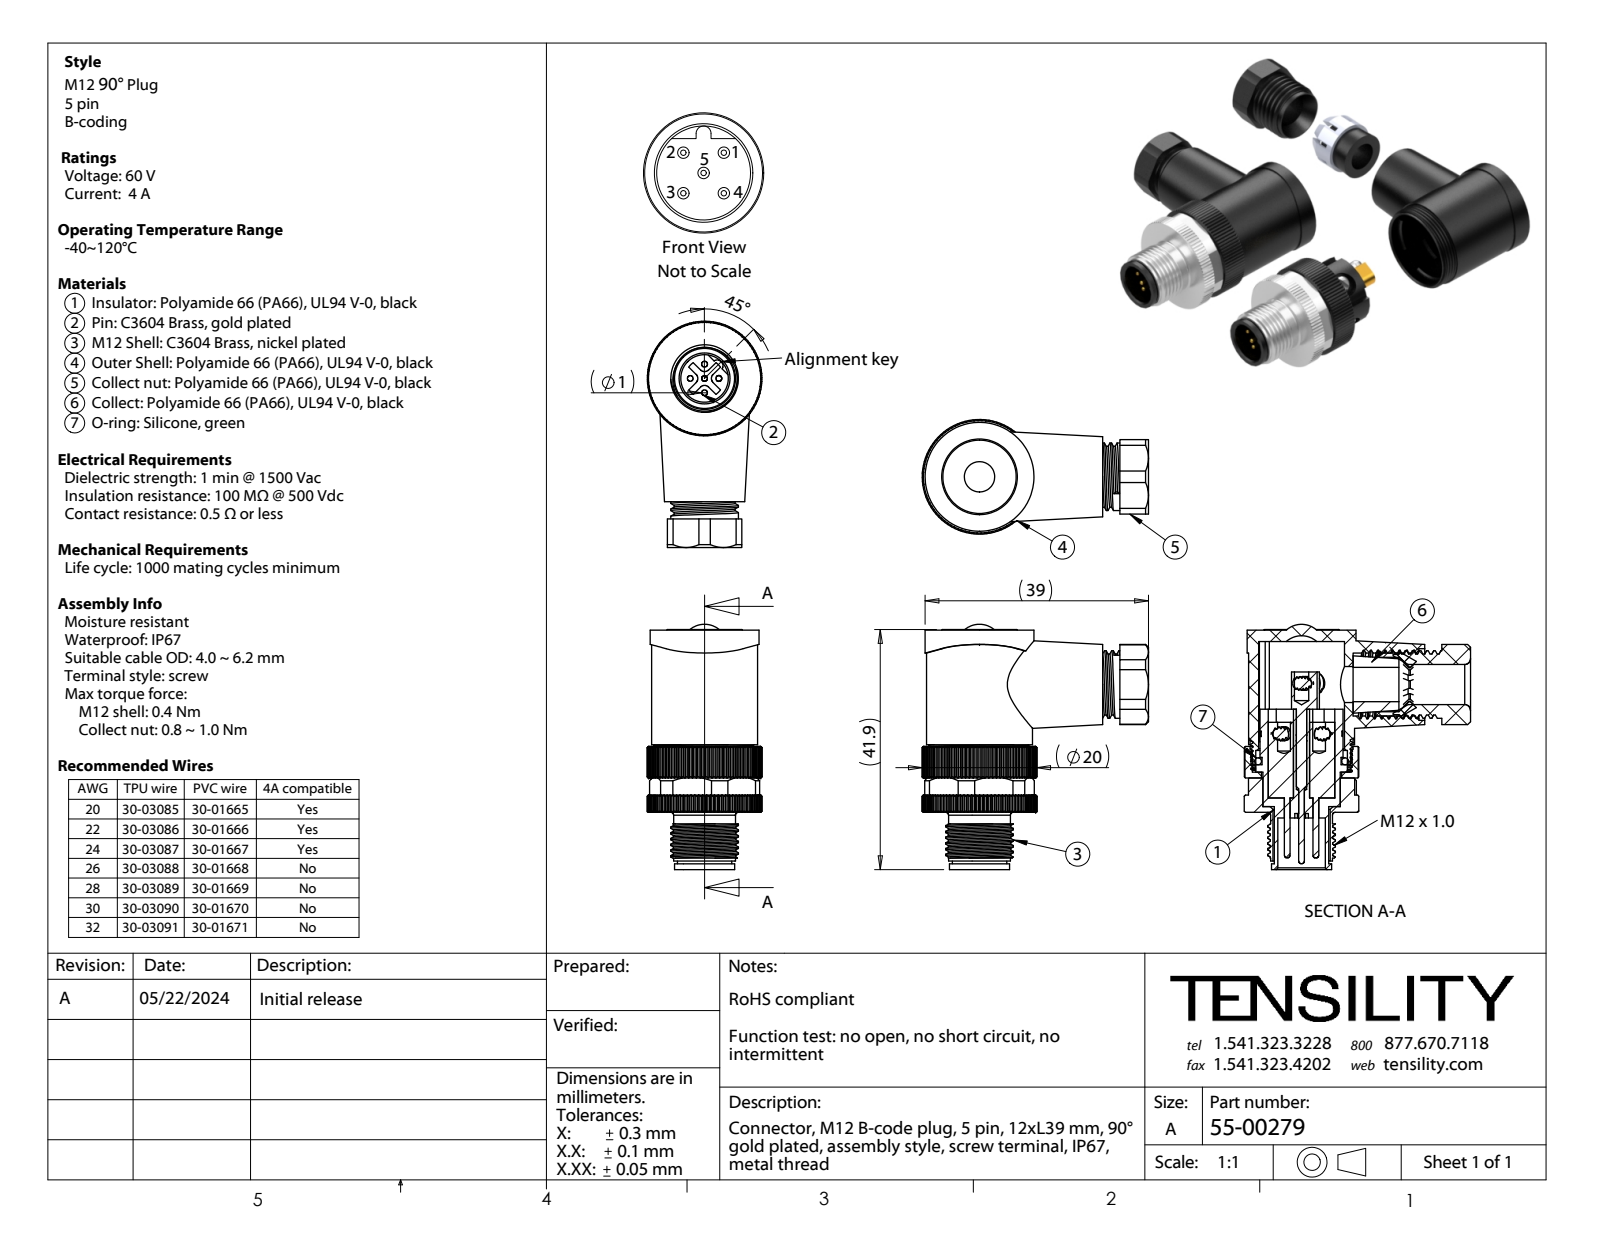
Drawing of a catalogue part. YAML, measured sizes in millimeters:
part_name: "55-00279-06; 55-00279-05; 55-00279-07; 55-00279-09 (+8 more)"
step_written_by: "SolidWorks 2021 (CONFIG_CONTROL_DESIGN)"
units: millimeters
bodies: {solids: 18, faces: 1649, planar: 574, cylindrical: 539, other: 536}
overall_size: [42.8, 39.5, 20]
volume: 9136
surface_area: 14240
round_holes:
  - {diameter: 2.5, count: 9}
  - {diameter: 1, count: 5}
  - {diameter: 2.05, count: 5}
  - {diameter: 5, count: 4}
  - {diameter: 6, count: 1}
  - {diameter: 6.3, count: 1}
  - {diameter: 7, count: 1}
  - {diameter: 8.3, count: 1}
  - {diameter: 9.5, count: 1}
  - {diameter: 10, count: 1}
  - {diameter: 11, count: 1}
  - {diameter: 12.5, count: 1}
round_bosses_or_shafts:
  - {diameter: 3.5, count: 5}
  - {diameter: 2.4, count: 5}
  - {diameter: 11.8, count: 2}
  - {diameter: 10.5, count: 2}
  - {diameter: 20, count: 1}
  - {diameter: 19, count: 1}
  - {diameter: 18.5, count: 1}
  - {diameter: 17.8, count: 1}
partial_cylinders:
  - {radius: 1, count: 5}
  - {radius: 1.75, count: 5}
  - {radius: 3.4, count: 1}
  - {radius: 6.45, count: 1}
  - {radius: 6.5, count: 1}
  - {radius: 7, count: 1}
  - {radius: 9.65, count: 1}
face_to_face_distances: [1, 6, 25.8, 2, 4.5, 7, 13.86, 31.8, 18, 3.5]
hole_center_spacings: [5.14, 5.13, 0.8, 2.5, 3.12, 3.54, 3.62, 4.34]
